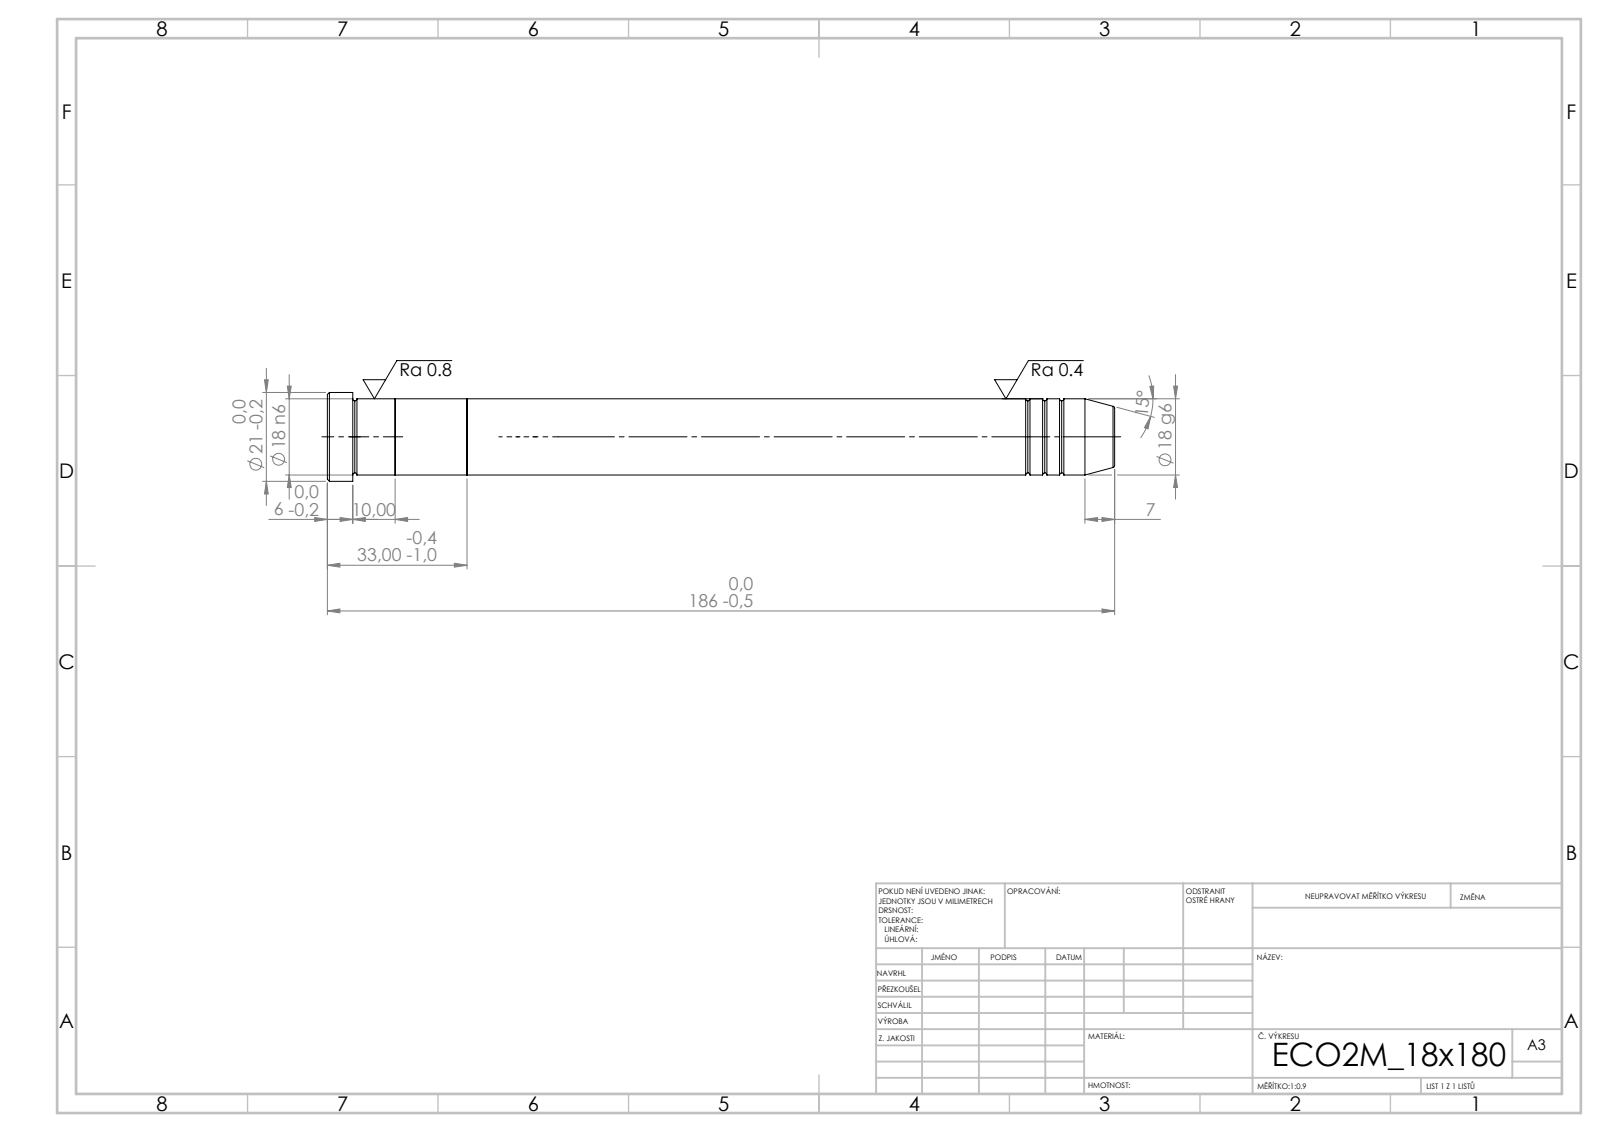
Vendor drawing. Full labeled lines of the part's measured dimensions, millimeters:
STEP written by: SolidWorks 2019 (CONFIG_CONTROL_DESIGN)
Units: millimetres
Bodies: 3 solids, 43 faces (7 planar, 14 cylindrical, 22 other)
Overall size (bounding box): 186 × 21 × 21
Volume: 47 441 mm³ · Surface area: 12 253 mm²
Round bosses / shafts (diameter × count): ⌀21 ×1, ⌀18 ×1
Main face-to-face distances: 17, 33, 16, 153, 170, 186, 180, 27, 10, 6
